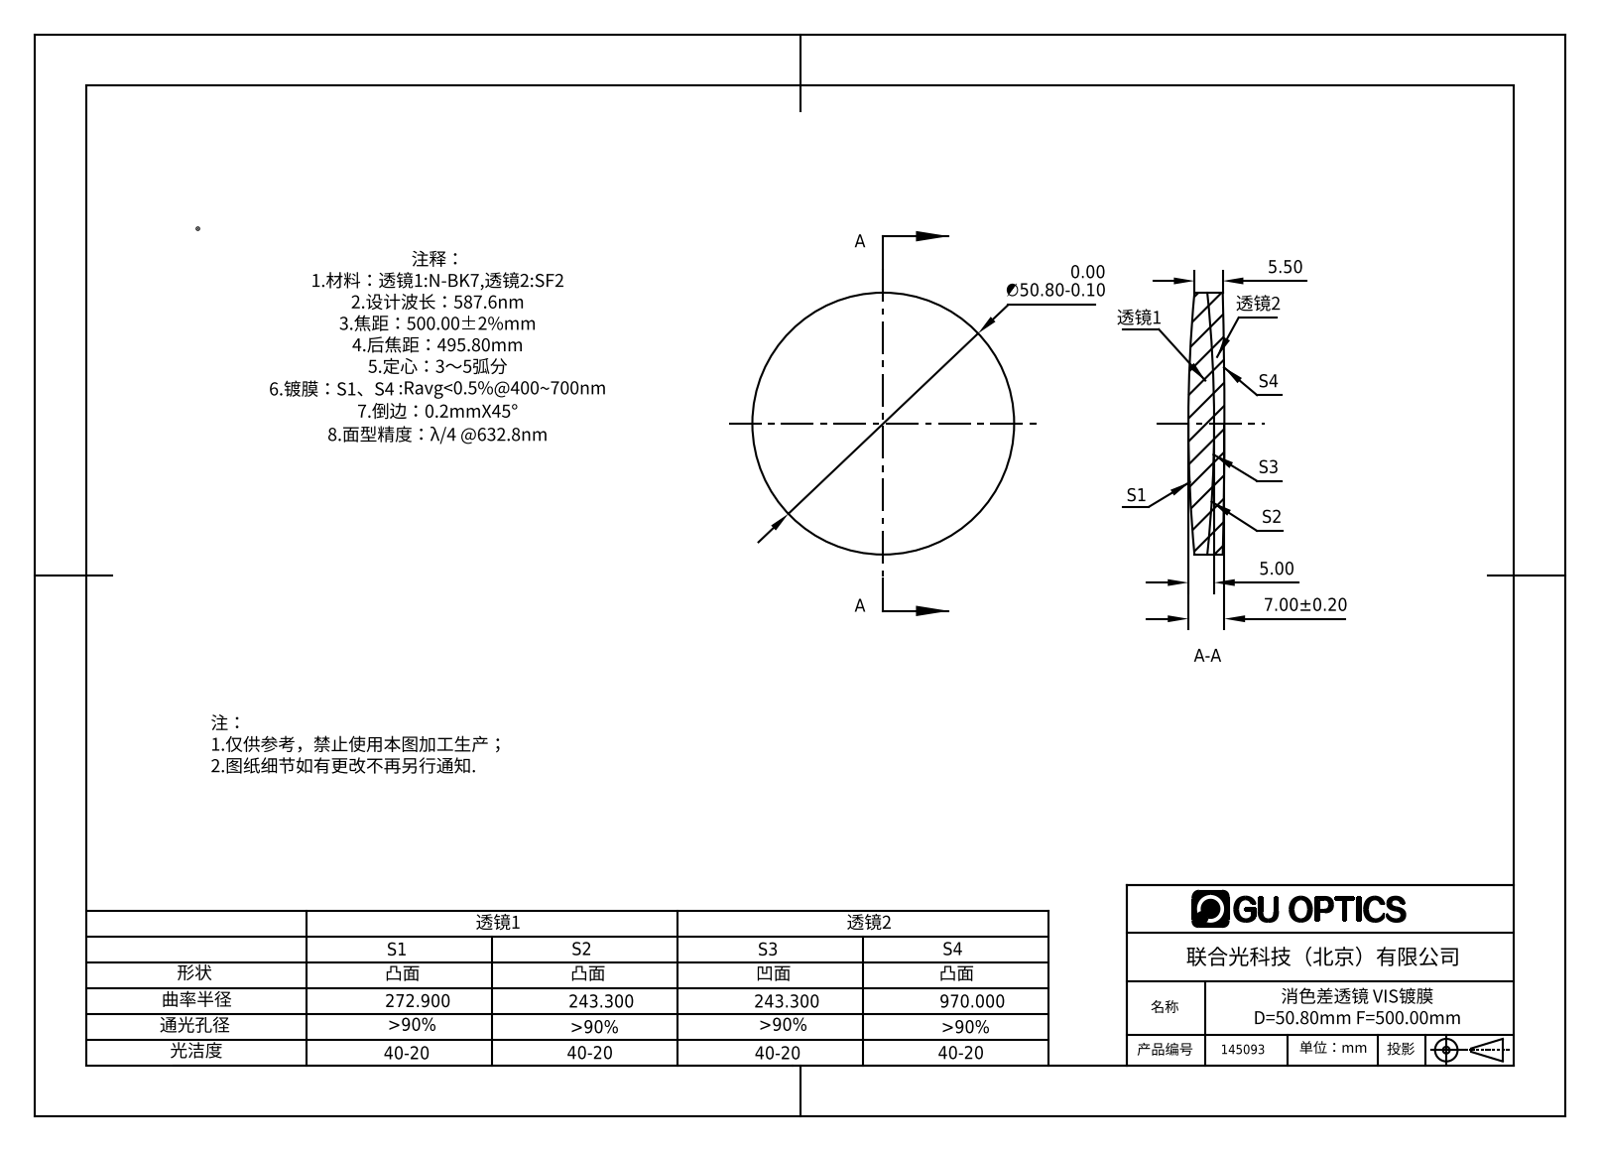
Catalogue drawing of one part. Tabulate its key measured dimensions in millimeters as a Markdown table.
| quantity | value |
| --- | --- |
| part name | 145093 |
| STEP written by | SolidWorks 2016 (AUTOMOTIVE_DESIGN) |
| units | millimeters |
| bodies | 2 solids, 12 faces (0 planar, 4 cylindrical, 8 other) |
| overall size | 50.8 × 50.8 × 7 |
| volume | 12 651 mm³ |
| surface area | 8 998 mm² |
| round bosses / shafts (diameter × count) | 50.8 × 1 |
